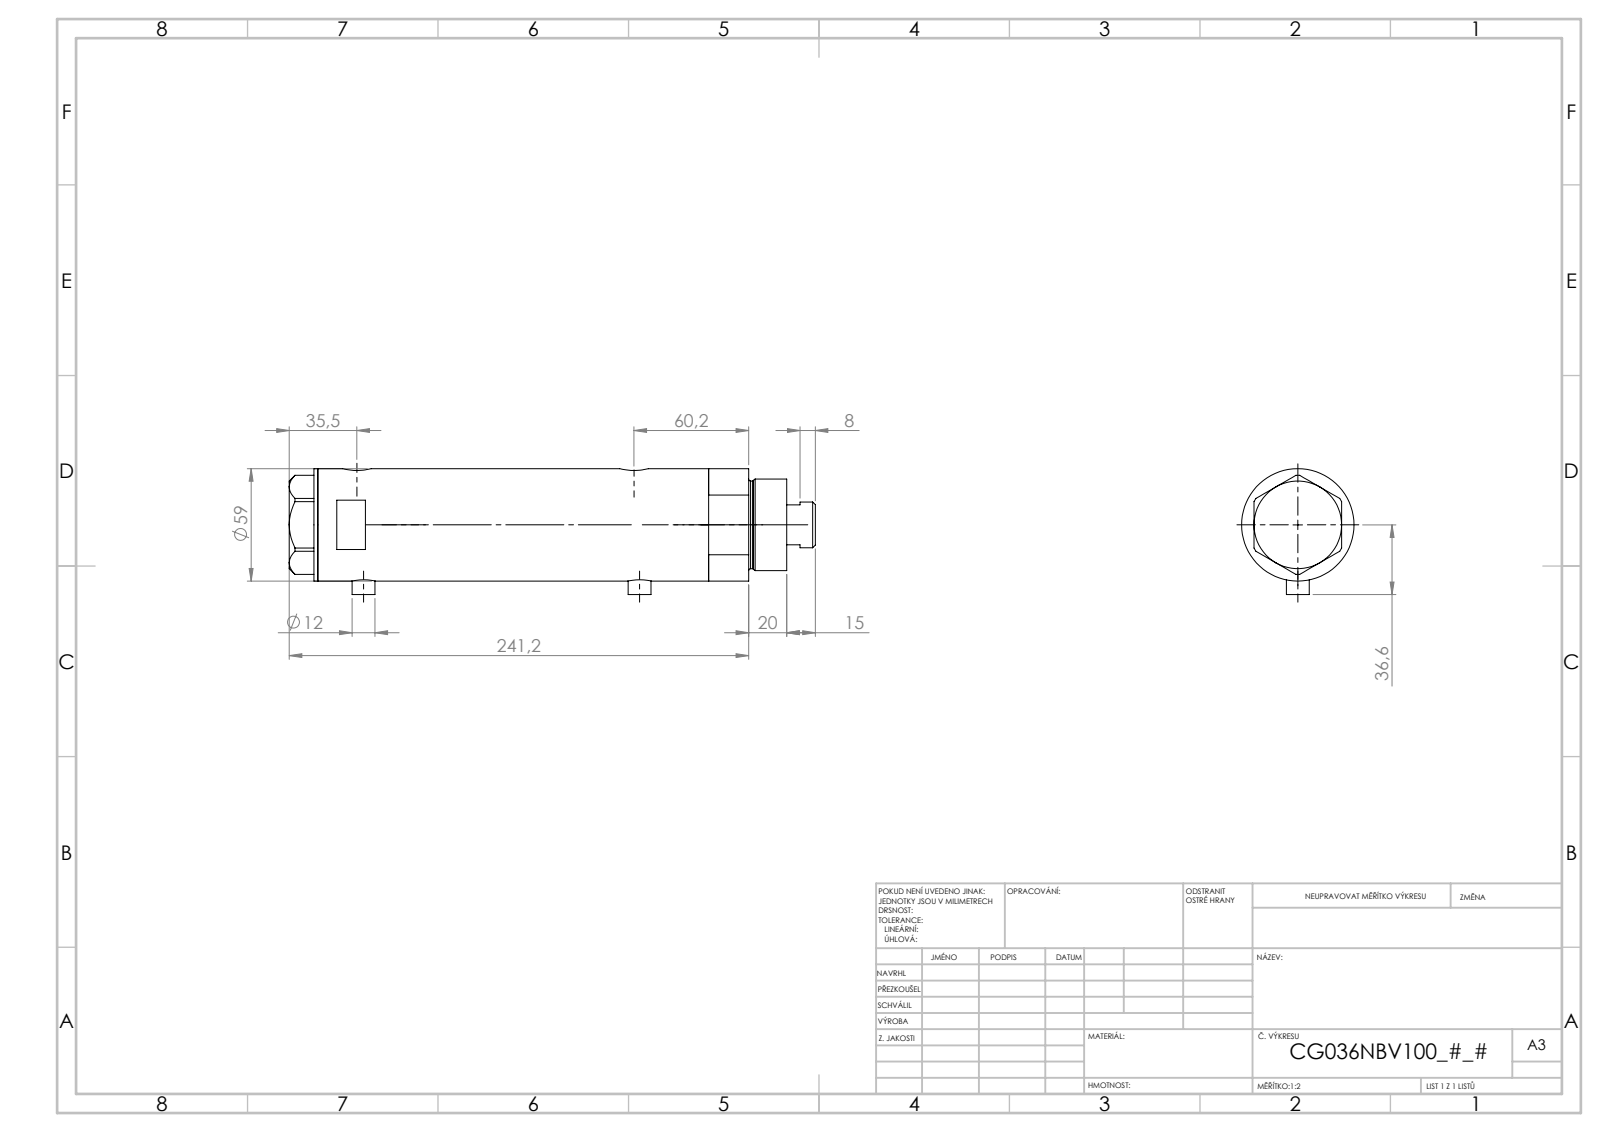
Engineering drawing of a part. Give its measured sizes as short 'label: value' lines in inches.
name: V270CG_FRONT; V270CG_BACK; V270CG_VC; V270CG_MIDDLE
written by: SolidWorks 2019 (CONFIG_CONTROL_DESIGN)
unit: in
bodies: 4 solids, 126 faces (53 planar, 53 cylindrical, 20 other)
size: 10.371 × 2.366 × 2.323
volume: 36.12 in³; area: 185.4 in²
holes: 2× ⌀0.197, 2× ⌀0.383, 2× ⌀0.492, 2× ⌀0.591, 1× ⌀0.335, 1× ⌀0.984, 1× ⌀1.043, 1× ⌀1.417, 1× ⌀1.575, 1× ⌀2.047
bosses: 2× ⌀0.472, 1× ⌀2.323, 1× ⌀1.89, 1× ⌀1.811, 1× ⌀0.945
face distances: 6.194, 0.925, 5.269, 0.591, 1.516, 6.785, 9.78, 9.19, 8.265, 2.995
hole spacings: 0.114, 0.138, 5.203, 5.317, 5.341, 5.455, 0.114, 0.115
